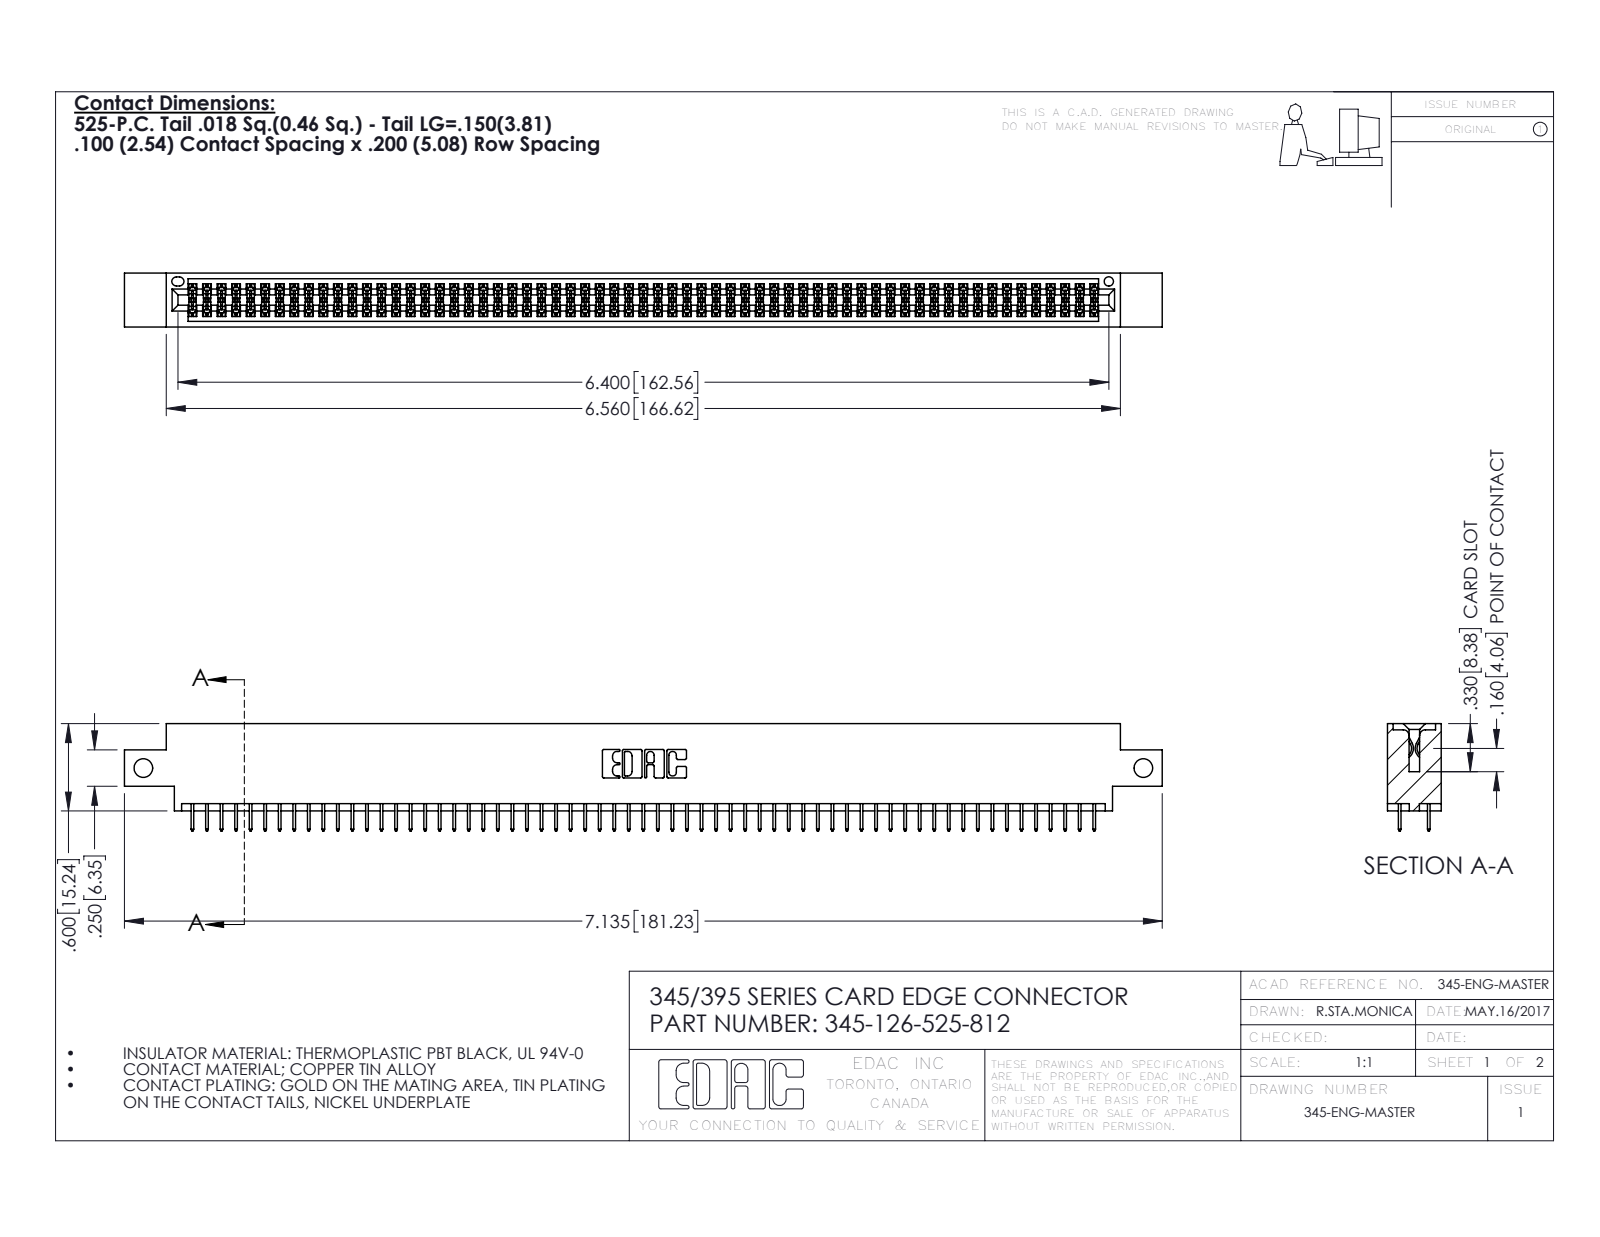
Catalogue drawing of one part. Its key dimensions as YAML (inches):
part_name: "345-292-001_345-293-125; 345-126-525-812; 345 Part_0.170 Offset - Side Mount"
step_written_by: "SolidWorks 2020 (CONFIG_CONTROL_DESIGN)"
units: inches
bodies: {solids: 127, faces: 6934, planar: 4998, cylindrical: 1936, other: 0}
overall_size: [7.135, 0.737, 0.37]
volume: 1.061
surface_area: 39.52
round_holes:
  - {diameter: 0.128, count: 2}
  - {diameter: 0.064, count: 1}
partial_cylinders:
  - {radius: 0.006, count: 189}
  - {radius: 0.01, count: 22}
  - {radius: 0.007, count: 6}
  - {radius: 0.031, count: 6}
  - {radius: 0.026, count: 3}
  - {radius: 0.014, count: 2}
  - {radius: 0.019, count: 2}
  - {radius: 0.022, count: 2}
face_to_face_distances: [0.072, 0.298, 0.37, 0.2, 0.098, 0.272, 0.025, 0.225, 0.175, 0.072]
hole_center_spacings: [6.875]
